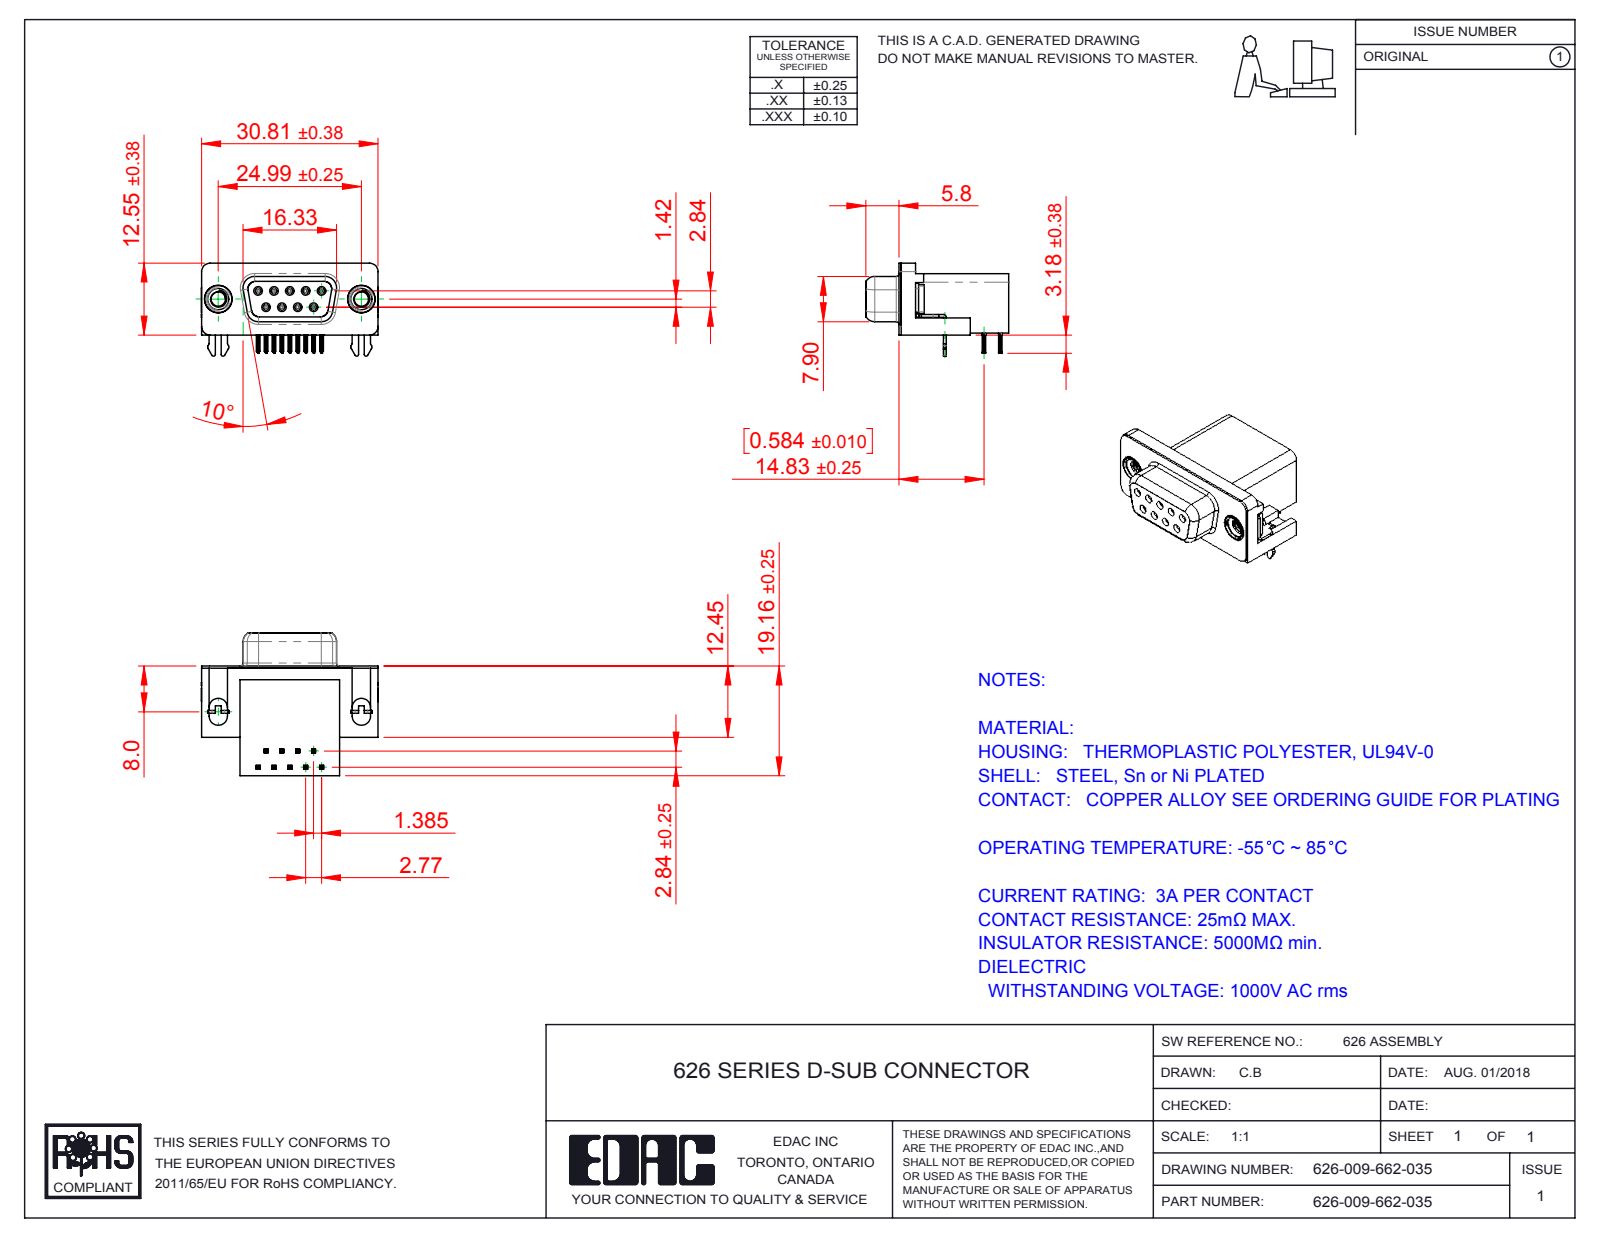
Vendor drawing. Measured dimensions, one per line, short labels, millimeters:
name: 626 Contact Top; 626 Housing_9 Socket; 626 2 Prong Board Lock; 626 Contact Bottom (+3 more)
written by: SolidWorks 2016 (CONFIG_CONTROL_DESIGN)
unit: mm
bodies: 15 solids, 1612 faces (716 planar, 428 cylindrical, 468 other)
size: 30.89 × 24.96 × 16.25
volume: 4 962 mm³; area: 5 800 mm²
holes: 9× ⌀0.8, 9× ⌀0.9, 2× ⌀2.5, 2× ⌀4, 2× ⌀4.8, 2× ⌀5
bosses: 9× ⌀1.2, 2× ⌀4.9, 2× ⌀4.75, 2× ⌀3.9
rounds: 72× R0.1, 36× R0.15, 18× R0.35, 18× R1, 10× R0.5, 9× R0.34, 8× R0.25, 8× R1.35
face distances: 0.4, 10.34, 0.35, 18.76, 19.16, 2.9, 2.5, 6.2, 16.26, 0.5
hole spacings: 3.16, 2.77, 5.54, 5.03, 5.04, 8.31, 7.48, 7.49
